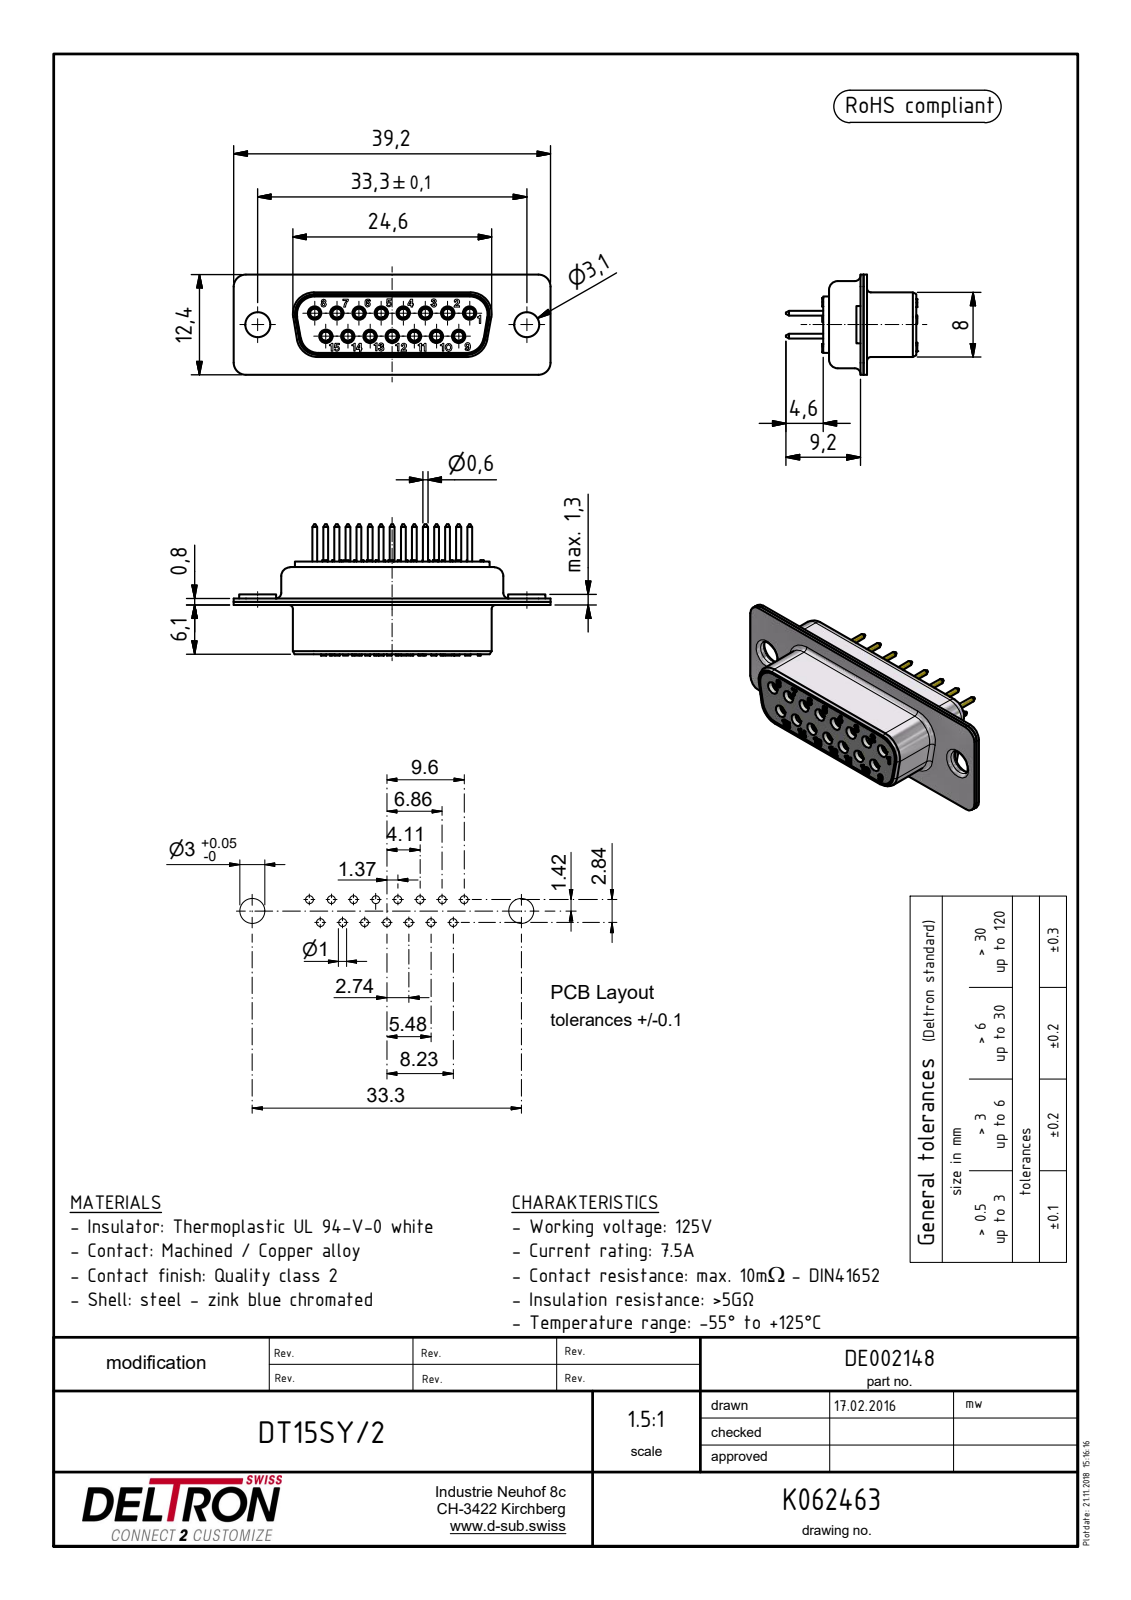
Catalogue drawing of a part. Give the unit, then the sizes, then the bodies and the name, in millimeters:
Units: millimetres
Overall size (bounding box): 39.2 × 16.25 × 12.4
Round holes (diameter × count): ⌀1.15 ×15, ⌀1.92 ×15, ⌀2.3 ×15, ⌀0.34 ×4, ⌀0.24 ×2, ⌀0.28 ×2, ⌀3.1 ×2, ⌀4.06 ×2
Round bosses / shafts (diameter × count): ⌀2.23 ×15, ⌀1.96 ×15, ⌀1.7 ×15, ⌀1.6 ×15, ⌀0.6 ×15, ⌀4.6 ×2, ⌀3.9 ×2
Partial cylindrical surfaces — rounded edges, fillets, slot ends (radius × count): R0.25 ×16, R2 ×12, R0.7 ×8, R1.1 ×8, R2.2 ×8, R0.34 ×4, R0.5 ×4, R0.9 ×4
Main face-to-face distances: 0.4, 0.8, 0.5, 1.4, 10.2, 7.1, 7.6, 7.5, 1.3, 9
Hole centre spacings: 3.15, 2.74, 5, 5.48, 7.42, 8.22, 10, 10.96
Volume: 2 310 mm³ · Surface area: 6 073 mm²
Bodies: 18 solids, 1195 faces (634 planar, 299 cylindrical, 262 other)
Part name (STEP PRODUCT): N00404_BG; R+B00895_BG; R+B00153_BG; R+B00144_BG (+1 more)
STEP written by: Autodesk Inventor 2015 (AUTOMOTIVE_DESIGN)
